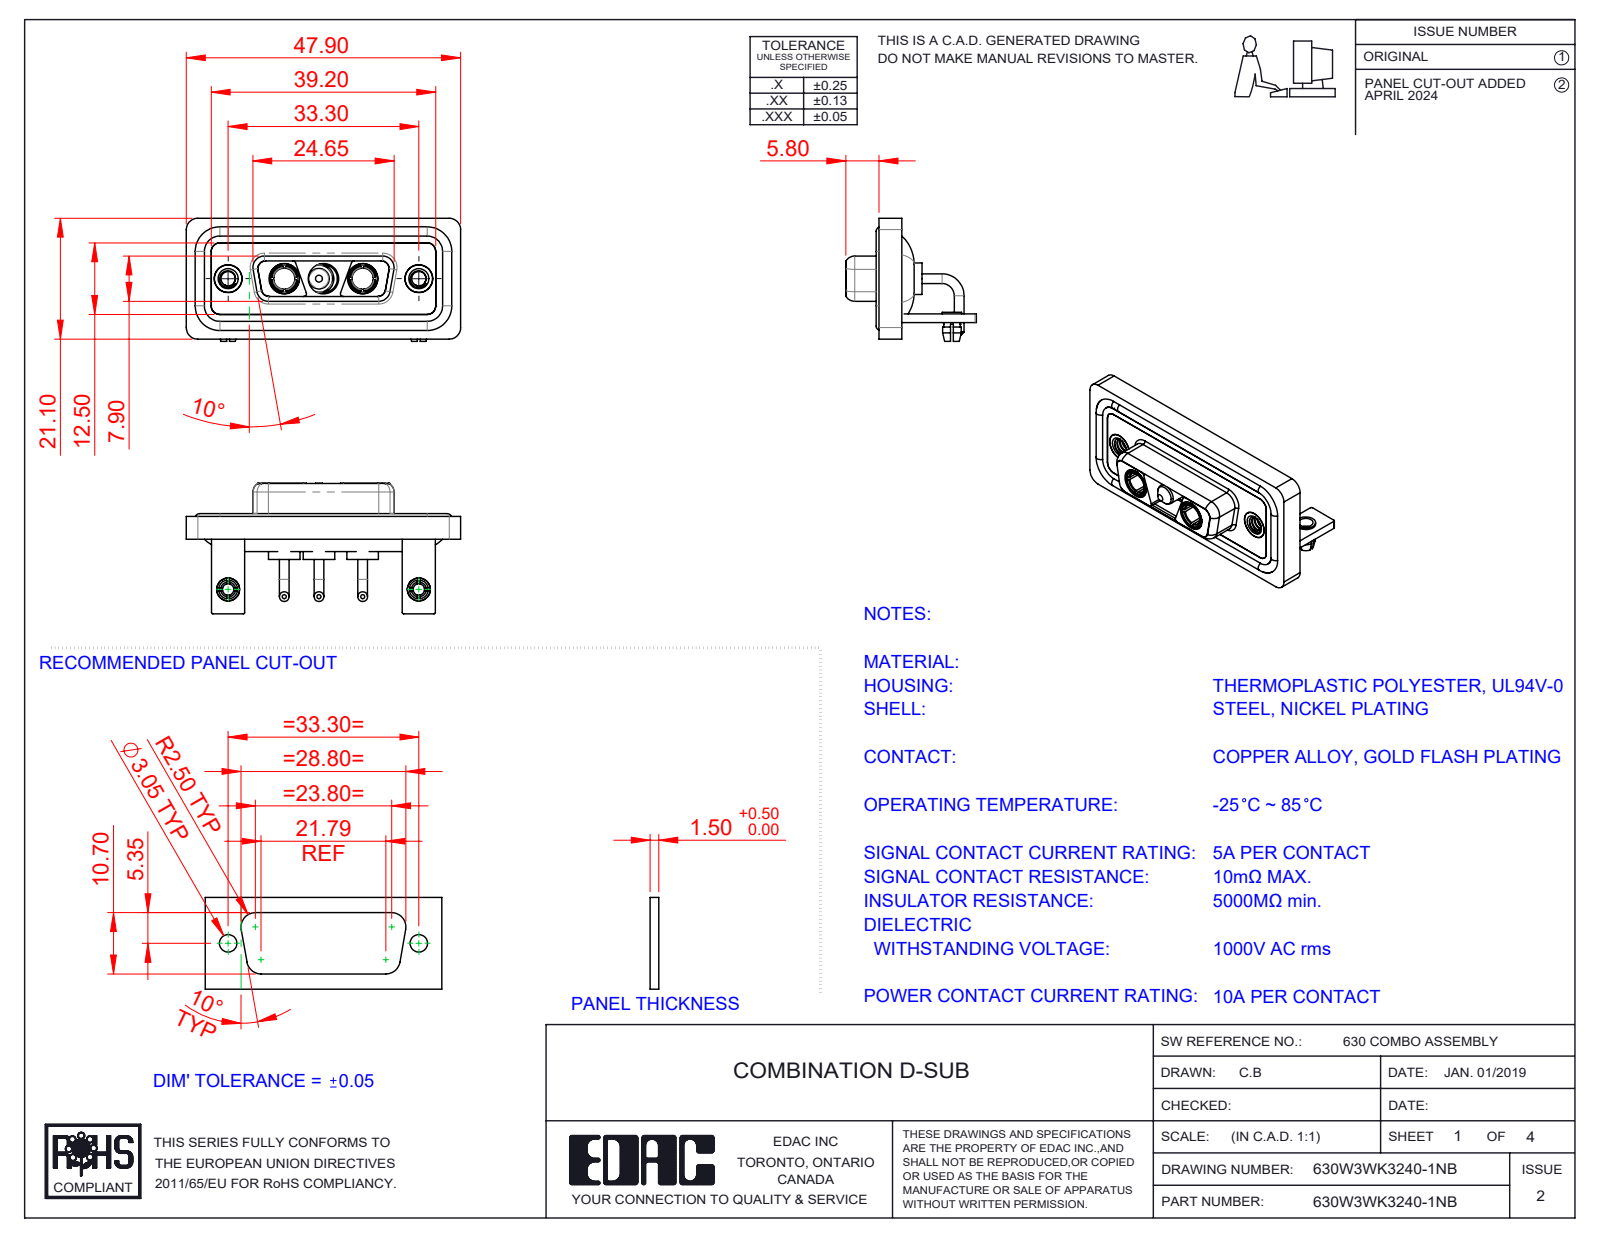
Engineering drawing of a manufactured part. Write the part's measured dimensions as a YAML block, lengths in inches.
part_name: "630Combo Stabilizer Bracket_50 Contacts; Power Socket_10A RA; 630Combo Housing_3WK3; 630Combo Board Lock_50 Contacts (+6 more)"
step_written_by: "SolidWorks 2023 (CONFIG_CONTROL_DESIGN)"
units: inches
bodies: {solids: 17, faces: 729, planar: 246, cylindrical: 318, other: 165}
overall_size: [1.886, 0.898, 0.846]
volume: 0.382
surface_area: 16.33
round_holes:
  - {diameter: 0.191, count: 5}
  - {diameter: 0.098, count: 4}
  - {diameter: 0.209, count: 3}
  - {diameter: 0.079, count: 2}
  - {diameter: 0.126, count: 2}
  - {diameter: 0.146, count: 2}
  - {diameter: 0.157, count: 2}
  - {diameter: 0.159, count: 2}
  - {diameter: 0.197, count: 2}
round_bosses_or_shafts:
  - {diameter: 0.067, count: 6}
  - {diameter: 0.063, count: 4}
  - {diameter: 0.217, count: 3}
  - {diameter: 0.205, count: 3}
  - {diameter: 0.187, count: 3}
  - {diameter: 0.148, count: 3}
  - {diameter: 0.195, count: 2}
  - {diameter: 0.195, count: 2}
partial_cylinders:
  - {radius: 0.079, count: 21}
  - {radius: 0.059, count: 18}
  - {radius: 0.01, count: 16}
  - {radius: 0.053, count: 12}
  - {radius: 0.02, count: 9}
  - {radius: 0.063, count: 8}
  - {radius: 0.024, count: 4}
  - {radius: 0.026, count: 4}
face_to_face_distances: [0.016, 0.114, 0.059, 0.146, 0.071, 0.043, 0.161, 0.063, 0.098, 0.055]
hole_center_spacings: [0.27, 0.386, 0.656, 0.925, 1.311, 0.539]
